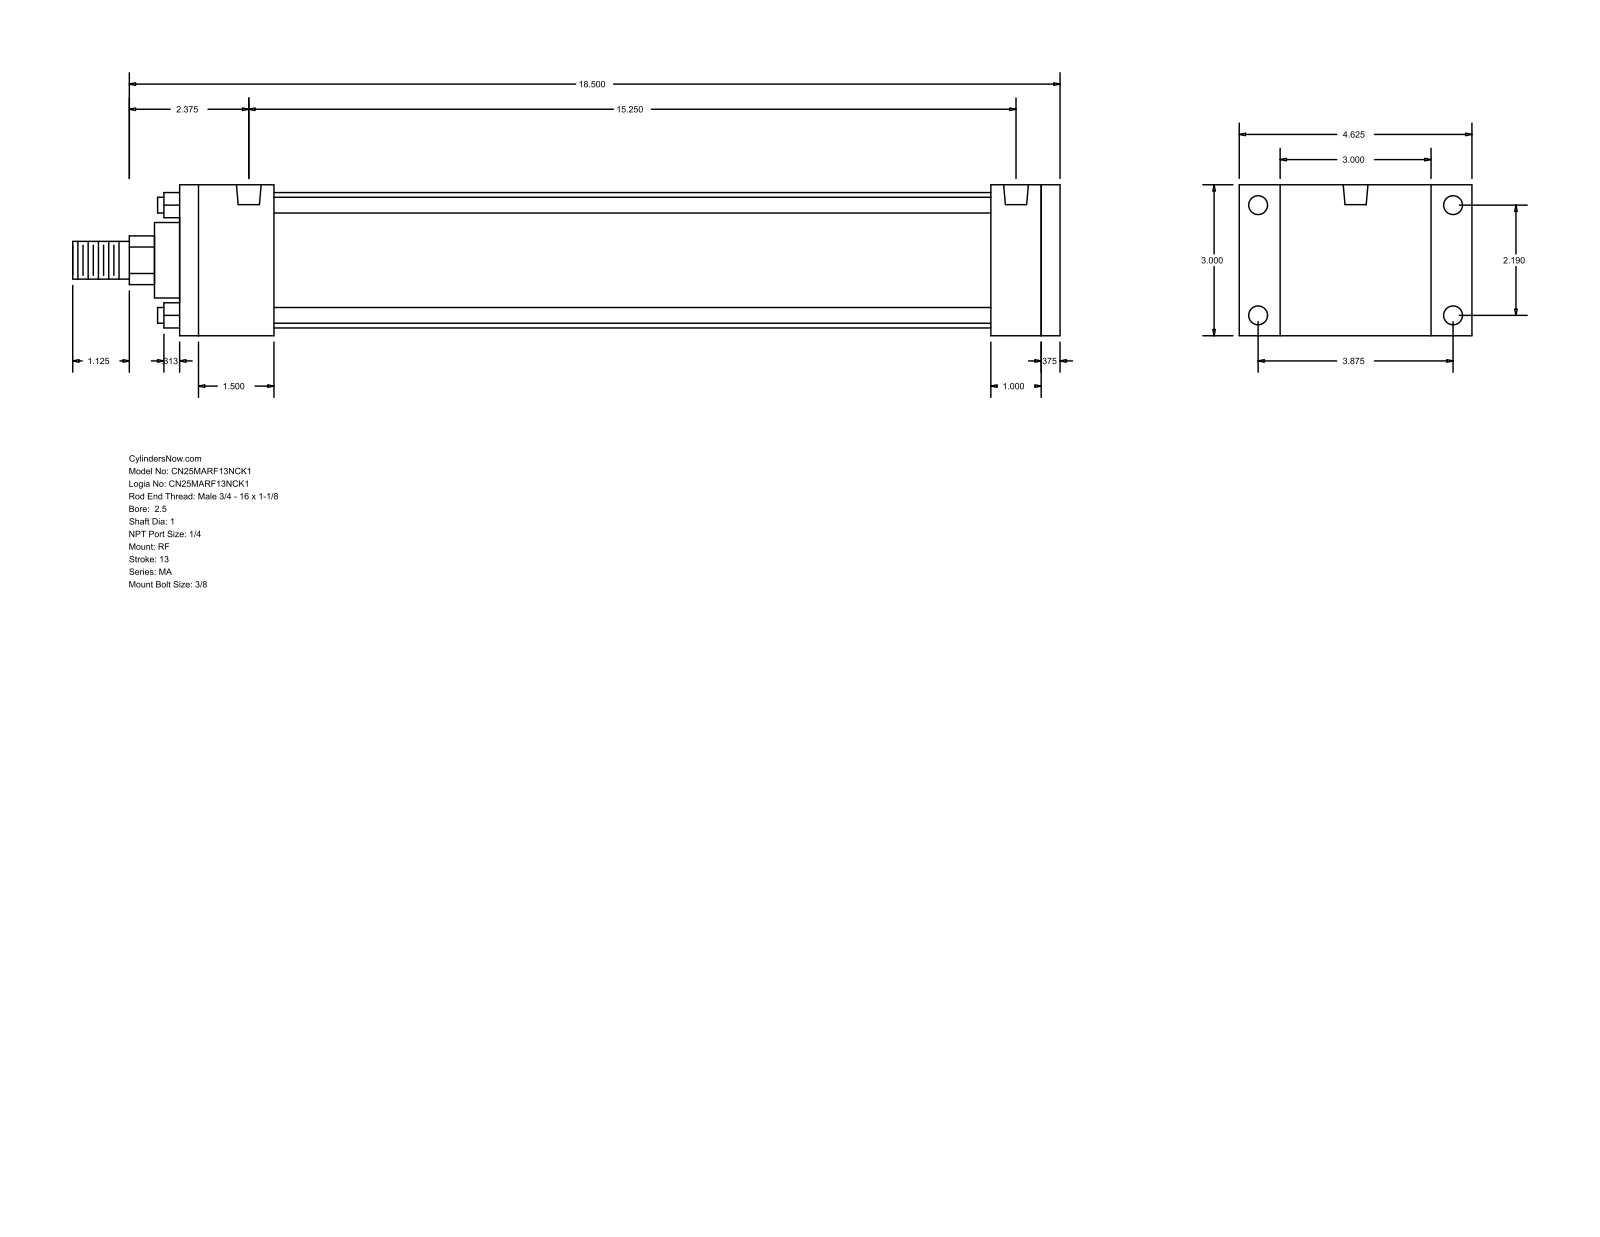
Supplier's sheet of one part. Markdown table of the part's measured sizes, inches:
| quantity | value |
| --- | --- |
| part name | MA_RF__0250_1 |
| STEP written by | GSSL Pune (CONFIG_CONTROL_DESIGN) |
| units | inches |
| bodies | 0 solids, 92 faces (64 planar, 28 cylindrical, 0 other) |
| overall size | 19.625 × 4.625 × 3 |
| round holes (diameter × count) | 0.313 × 4, 0.375 × 4, 0.492 × 2 |
| round bosses / shafts (diameter × count) | 0.313 × 4, 2.69 × 1, 1.5 × 1, 1 × 1, 0.75 × 1 |
| partial cylindrical surfaces (radius × count) | 0.484 × 1 |
| main face-to-face distances | 3, 17.5, 17.125, 0.375, 1, 1.875, 16.125, 14.25, 15.25, 15.625 |
| hole center spacings | 2.19, 3.875, 4.451, 15.25 |
